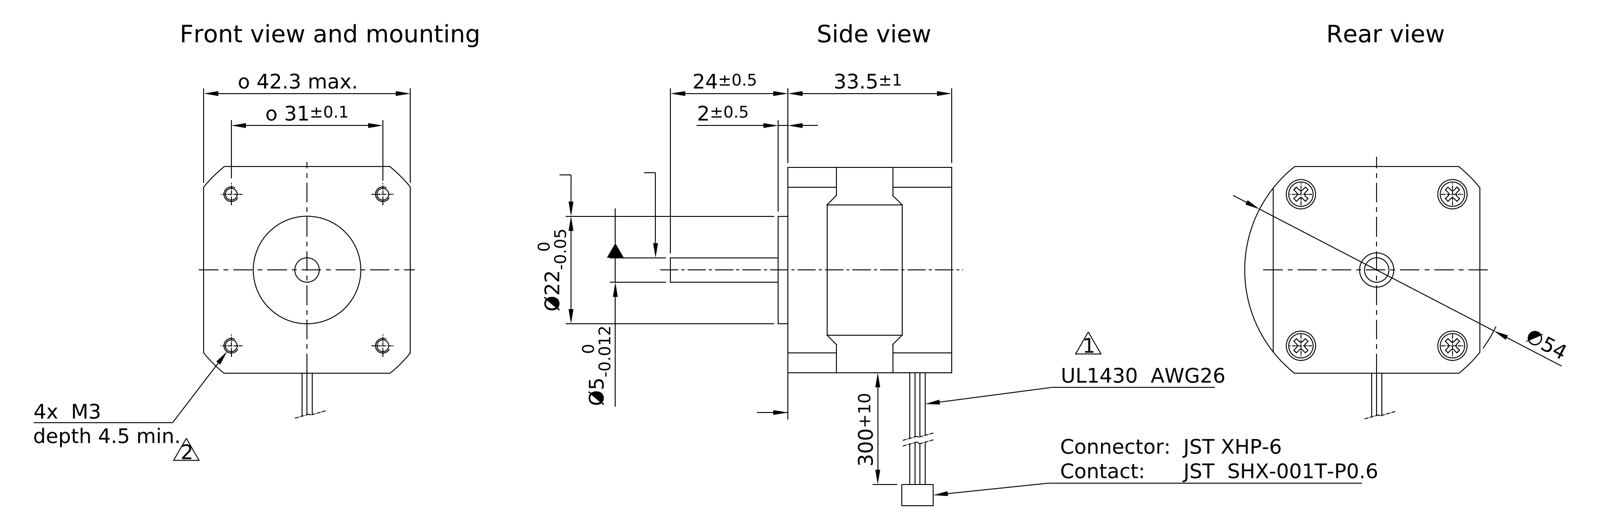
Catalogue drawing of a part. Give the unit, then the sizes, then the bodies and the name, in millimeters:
Units: millimetres
Overall size (bounding box): 57.5 × 54 × 42
Round holes (diameter × count): ⌀1 ×6, ⌀2.46 ×4, ⌀2.7 ×4, ⌀6 ×4, ⌀5 ×1, ⌀7 ×1, ⌀10 ×1
Round bosses / shafts (diameter × count): ⌀2.5 ×4, ⌀2.22 ×4, ⌀22 ×1
Partial cylindrical surfaces — rounded edges, fillets, slot ends (radius × count): R2 ×8, R27 ×1
Main face-to-face distances: 16.3, 42, 9, 25.3, 33.5, 24.5, 8.2, 2, 10.2, 48.08
Hole centre spacings: 1, 1.41, 21.92, 31, 2, 2.24, 43.84
Volume: 57 828 mm³ · Surface area: 17 724 mm²
Bodies: 14 solids, 192 faces (97 planar, 70 cylindrical, 25 other)
Part name (STEP PRODUCT): ST4209S...-A
STEP written by: Autodesk Inventor 2017 (AUTOMOTIVE_DESIGN)
